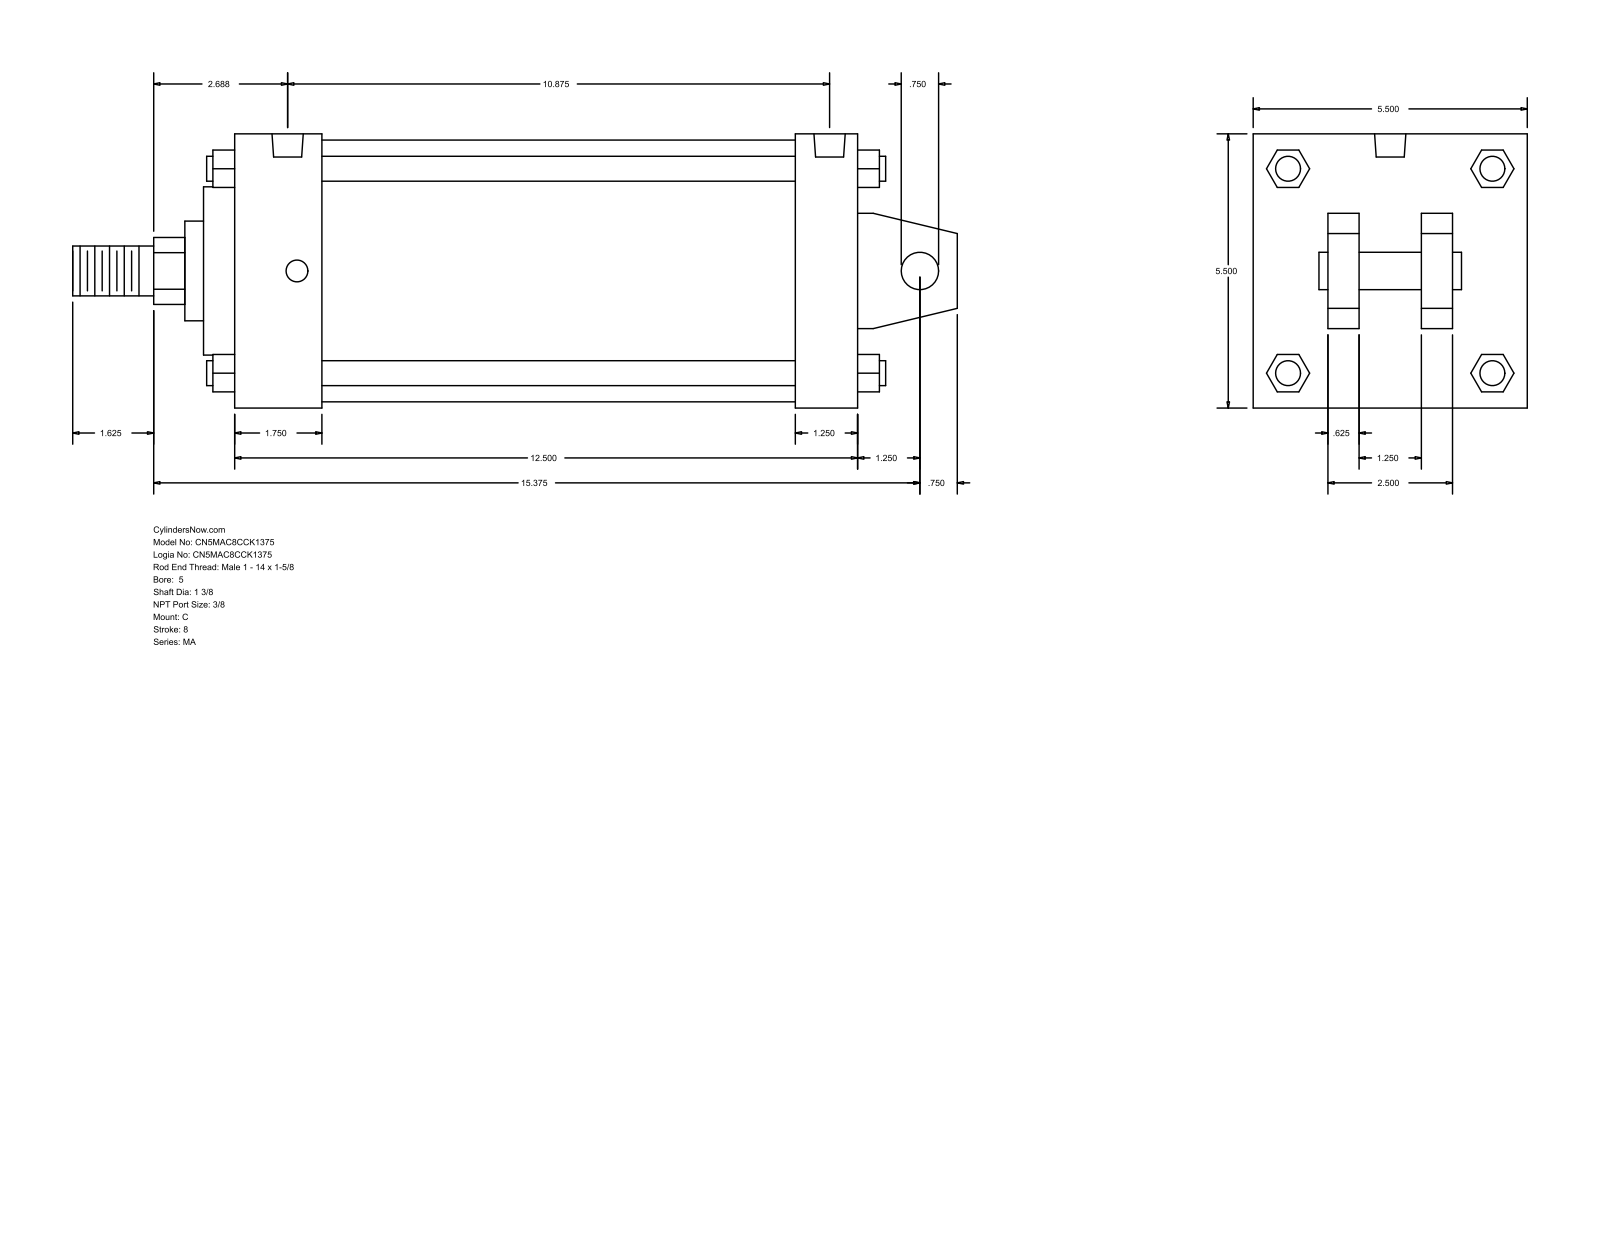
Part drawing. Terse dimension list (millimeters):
name: MA_C__0500_1.375
written by: GSSL Pune (CONFIG_CONTROL_DESIGN)
unit: mm
bodies: 0 solids, 141 faces (109 planar, 32 cylindrical, 0 other)
size: 450.85 × 139.7 × 139.7
holes: 4× ⌀11.11, 2× ⌀15.93
bosses: 4× ⌀12.7, 1× ⌀133.35, 1× ⌀85.72, 1× ⌀50.8, 1× ⌀34.92, 1× ⌀25.4, 1× ⌀19.05
rounds: 1× R17.06
face distances: 139.7, 317.5, 15.87, 285.75, 31.75, 44.45, 241.3, 273.05, 53.97, 38.1
hole spacings: 266.7, 4.76, 4.77, 271.46, 271.47, 276.23
